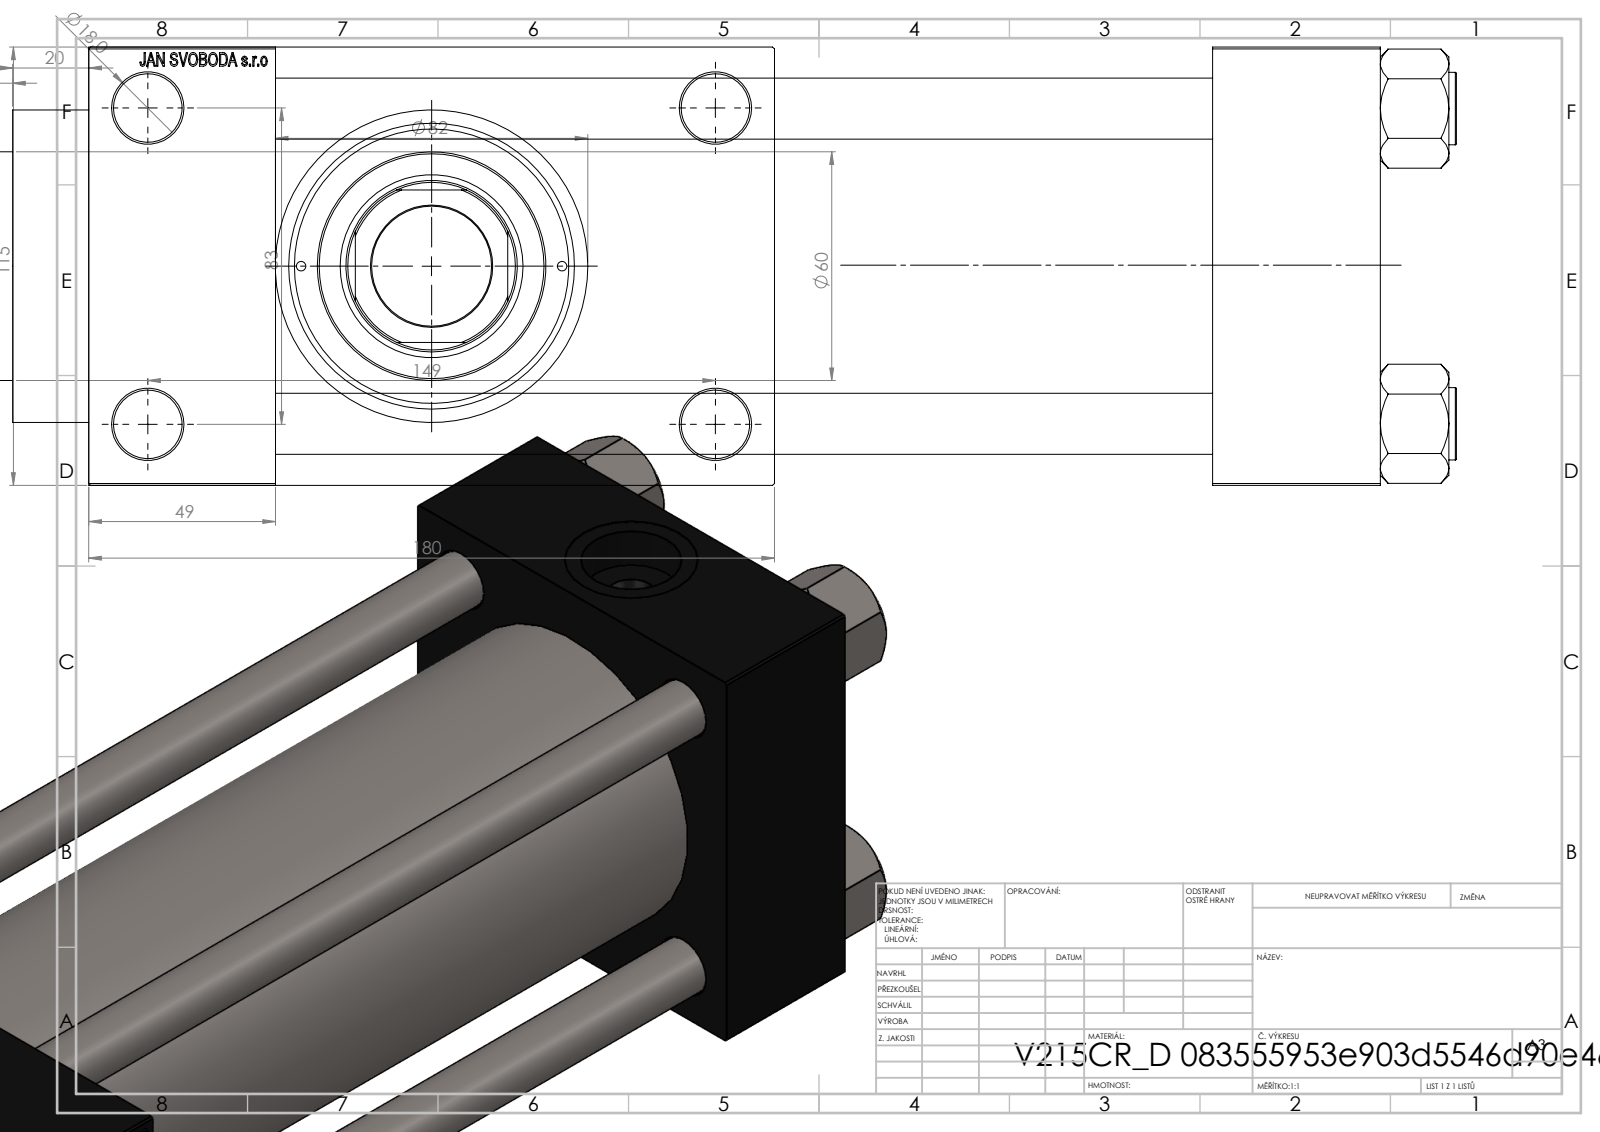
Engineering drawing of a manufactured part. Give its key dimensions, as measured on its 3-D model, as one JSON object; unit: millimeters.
{"part_name": "V215CR_VCP_D; V215CR_D_TYCINKA; V215_VC_A; NUT_M5_D (+1 more)", "step_written_by": "SolidWorks 2019 (CONFIG_CONTROL_DESIGN)", "units": "millimeters", "bodies": {"solids": 11, "faces": 1160, "planar": 547, "cylindrical": 93, "other": 520}, "overall_size": [410, 180, 115], "volume_mm3": 2593000, "surface_area_mm2": 455149, "round_holes": [[16, 4], [18, 4], [2.5, 2], [7, 2], [26.44, 2], [35, 2], [31.5, 1], [45, 1], [48, 1], [61, 1], [72, 1], [80, 1]], "round_bosses_or_shafts": [[19, 4], [86, 1], [82, 1], [60, 1]], "partial_cylinders_radius": [[22, 1]], "face_to_face_distances": [115, 246, 295, 49, 44, 290, 339, 32.5, 147.5, 180], "hole_center_spacings": [33.15, 41.96, 57.81, 58.48, 82.7, 85.28, 86.17, 89.24]}
